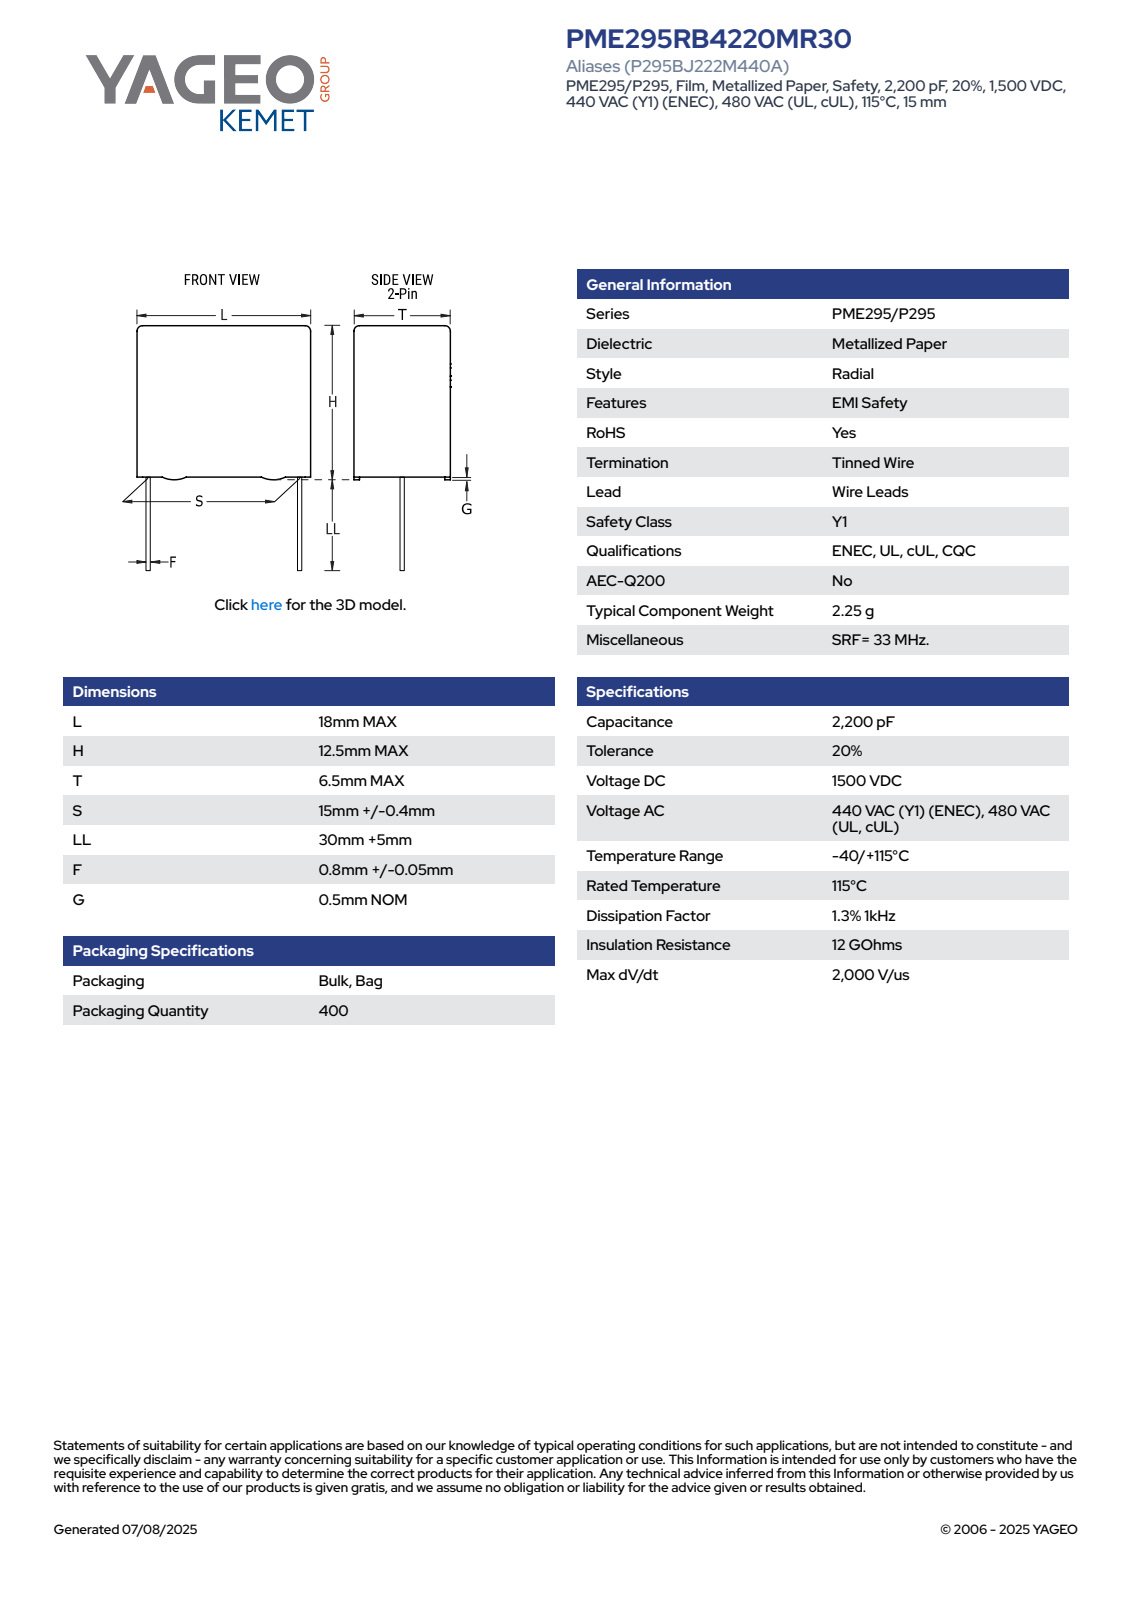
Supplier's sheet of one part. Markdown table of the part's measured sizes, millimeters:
| quantity | value |
| --- | --- |
| part name | CFR_RBG_18X12.5X6.5_L18H12.5T6.5S15LL35F0.85G0.5 |
| STEP written by | SolidWorks 2014 (AUTOMOTIVE_DESIGN) |
| units | millimeters |
| bodies | 4 solids, 89 faces (81 planar, 8 cylindrical, 0 other) |
| overall size | 47.5 × 18 × 6.5 |
| volume | 1 444 mm³ |
| surface area | 1 049 mm² |
| round bosses / shafts (diameter × count) | 0.85 × 2 |
| partial cylindrical surfaces (radius × count) | 0.5 × 4 |
| main face-to-face distances | 6.5, 12, 18, 0.37, 6.13, 0.5, 12.5, 5.76, 35, 35.5 |
